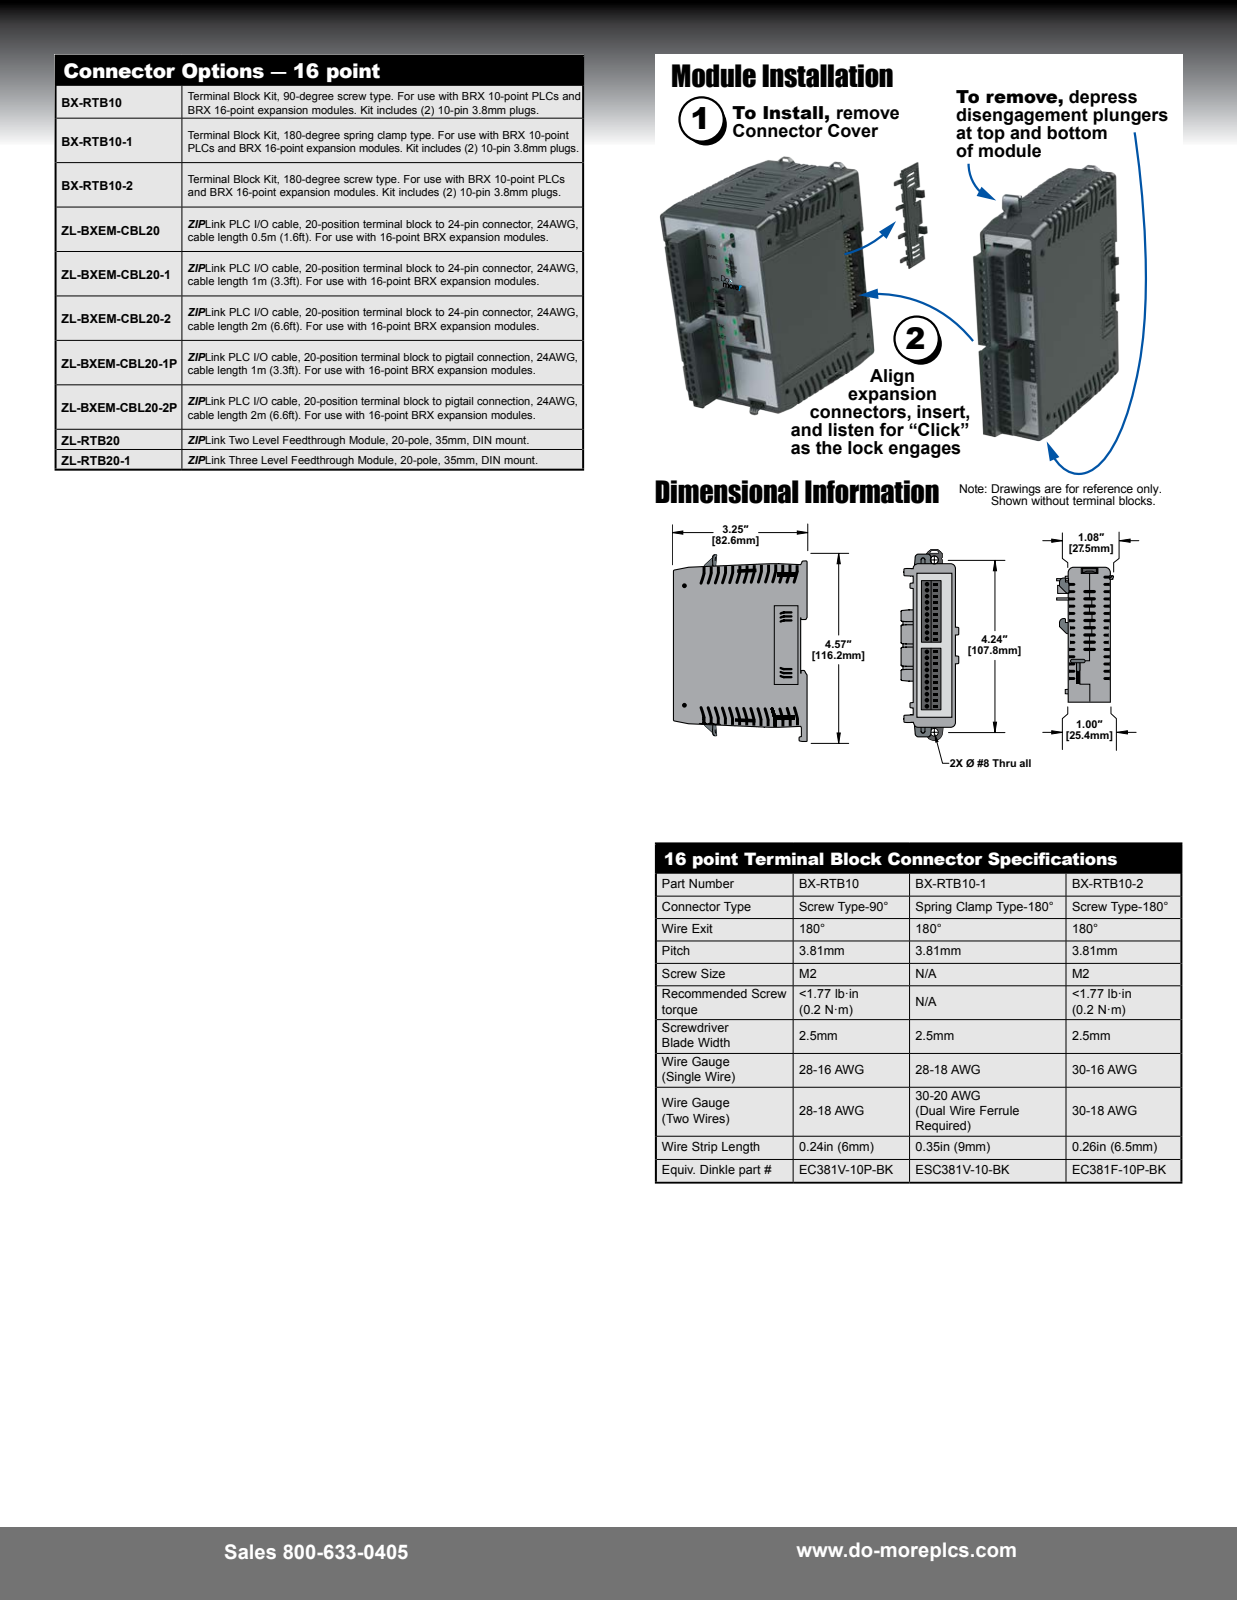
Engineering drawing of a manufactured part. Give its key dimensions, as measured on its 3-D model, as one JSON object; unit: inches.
{"part_name": "BX-16TDY2", "step_written_by": "SolidWorks 2024 (AUTOMOTIVE_DESIGN)", "units": "inches", "bodies": {"solids": 89, "faces": 5216, "planar": 3341, "cylindrical": 659, "other": 1216}, "overall_size": [4.586, 3.25, 1.402], "volume_in3": 11.6, "surface_area_in2": 72.92, "round_holes": [[0.047, 2], [0.065, 2], [0.118, 2], [0.118, 2], [0.199, 1]], "round_bosses_or_shafts": [[0.062, 2], [0.059, 2]], "partial_cylinders_radius": [[0.005, 102], [0.008, 101], [0.01, 47], [0.02, 30], [0.005, 24], [0.062, 20], [0.117, 14], [0.039, 13]], "face_to_face_distances": [1, 3.211, 3.231, 0.02, 0.475, 0.039, 0.157, 3.053, 3.073, 0.1], "hole_center_spacings": [0.1, 0.824, 0.919, 1.3, 2.093, 2.193, 2.585, 2.617]}
